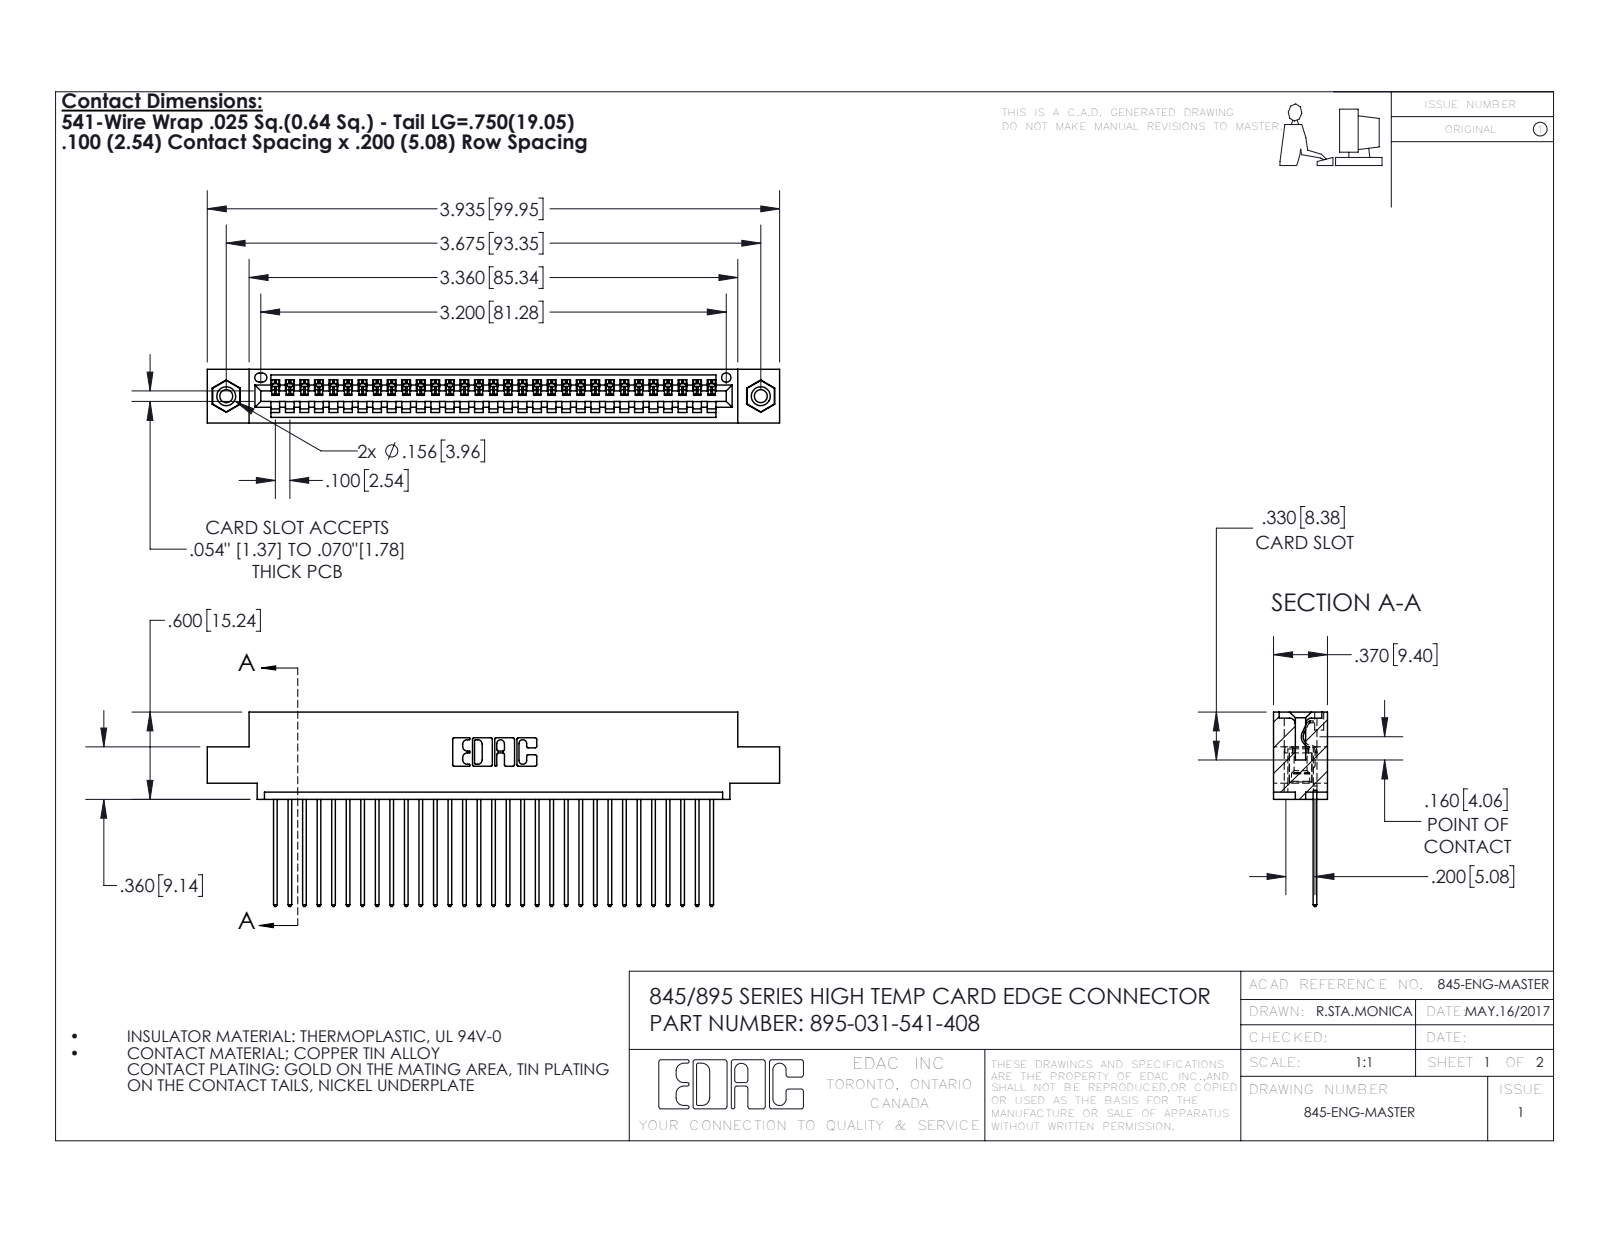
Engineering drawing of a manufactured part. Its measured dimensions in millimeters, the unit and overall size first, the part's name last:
Units: millimetres
Overall size (bounding box): 99.9 × 34 × 9.4
Round holes (diameter × count): ⌀2.3 ×2, ⌀3.2 ×2, ⌀4 ×2, ⌀1.6 ×1
Round bosses / shafts (diameter × count): ⌀3.9 ×2
Partial cylindrical surfaces — rounded edges, fillets, slot ends (radius × count): R0.2 ×62, R0.3 ×62, R0.3 ×22, R0.2 ×6, R0.8 ×6, R0.7 ×3, R0.8 ×2, R1 ×2
Main face-to-face distances: 1.8, 7.6, 2.5, 6.9, 0.6, 9.4, 5.1, 5.7, 3.8, 1.8
Hole centre spacings: 6.9, 87.4, 93.3
Volume: 9 420 mm³ · Surface area: 13 080 mm²
Bodies: 34 solids, 1988 faces (1356 planar, 616 cylindrical, 16 other)
Part name (STEP PRODUCT): 345-292-001_345-293-141; 395-031-541-408; 345 Part_0.110 Offset - 0.156 Dia-TI; 345-250-001_345-250-003-102
STEP written by: SolidWorks 2016 (CONFIG_CONTROL_DESIGN)
